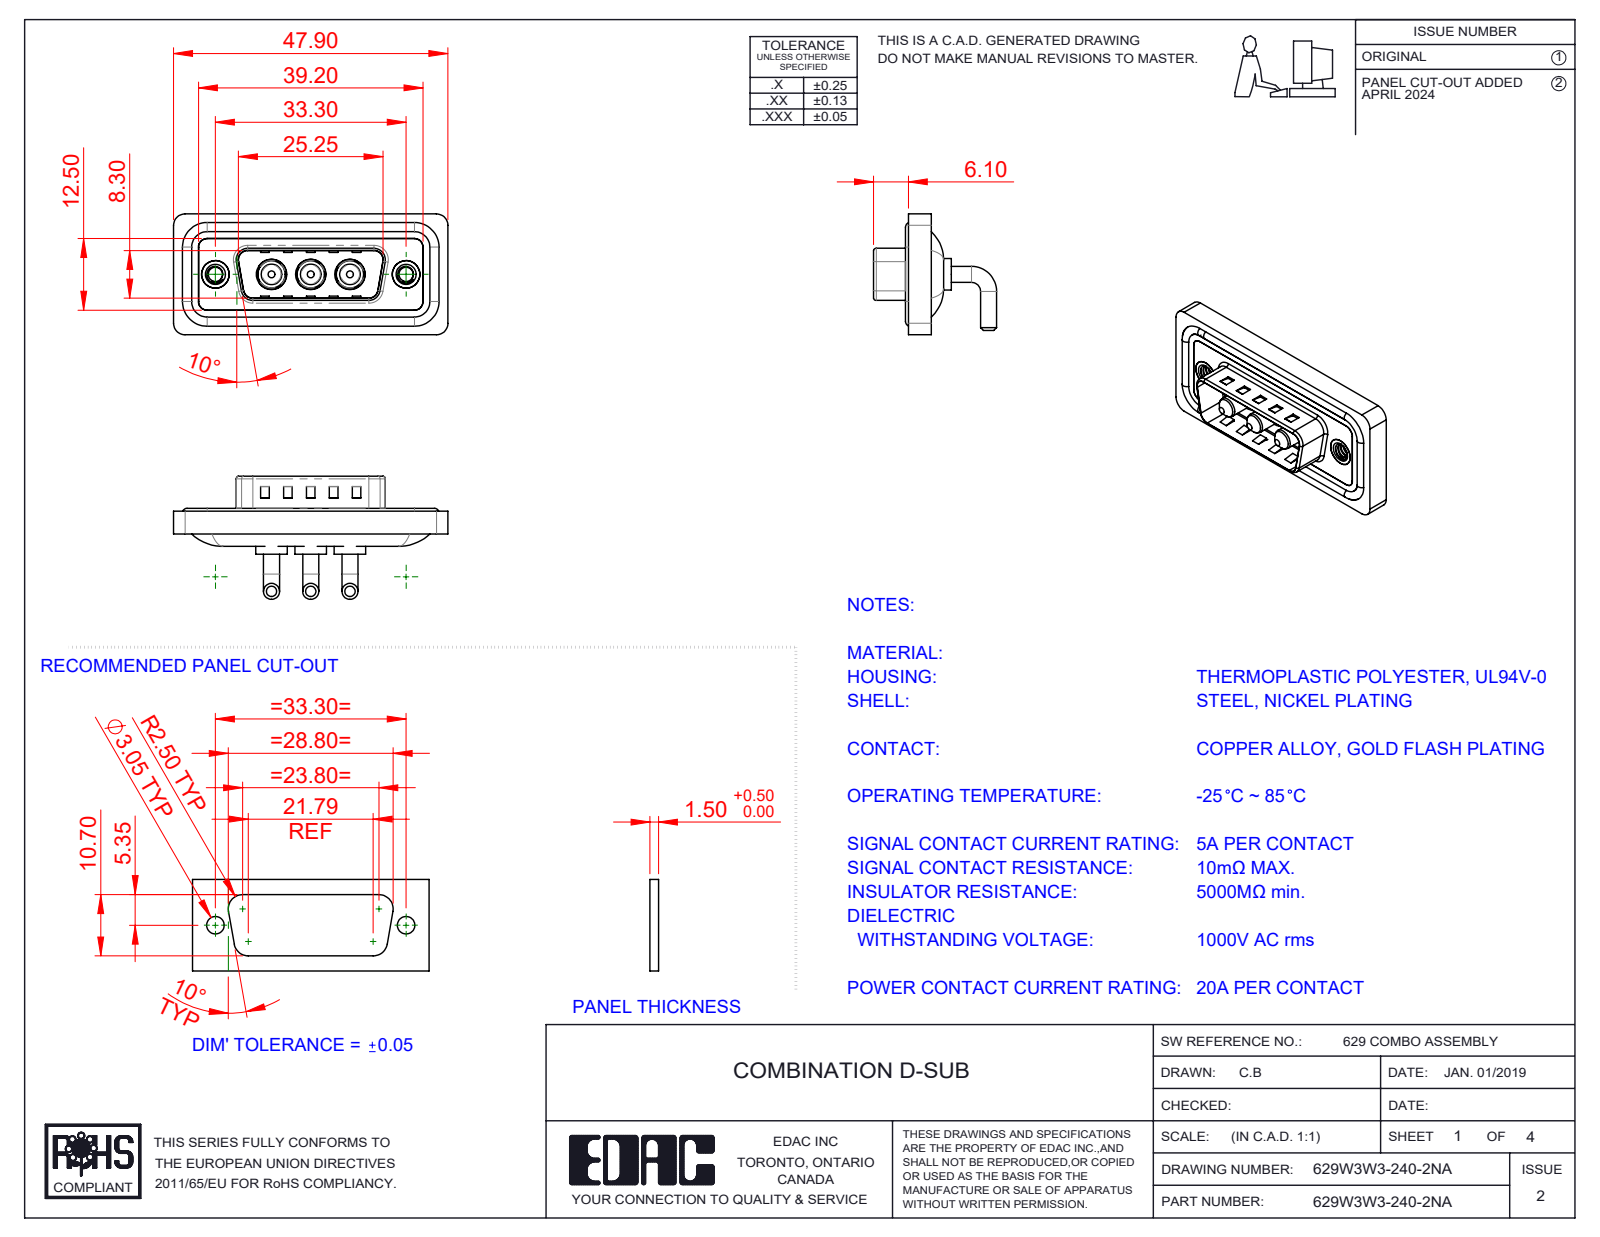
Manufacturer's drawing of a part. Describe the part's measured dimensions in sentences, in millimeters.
The part is named "629Combo Shell Rear_15 Contacts; 629Combo Shell Front_15 Contacts; 629W3W3-140-2NA; 629Combo Waterproof Housing_15 Contacts (+3 more)". Its 3-D file was written by "SolidWorks 2023 (CONFIG_CONTROL_DESIGN)". It is 13 solids with 570 faces: 207 planar, 245 cylindrical and 118 other. Overall it measures 47.9 by 21.5 by 21.1 millimeters. Its volume is 5 782 cubic millimeters and its surface area 9 040 square millimeters. Round holes: 3 of diameter 4.85, 3 of diameter 5.3, 2 of diameter 2.5, 2 of diameter 4, 2 of diameter 4.8, 2 of diameter 5. Round bosses or shafts: 6 of diameter 2.8, 4 of diameter 1.6, 3 of diameter 5.5, 3 of diameter 5.2, 3 of diameter 4.75, 3 of diameter 3.75, 3 of diameter 3.6, 2 of diameter 4.9. Partial cylindrical surfaces (rounded edges, fillets, slot ends): 20 of radius 2, 18 of radius 1.5, 8 of radius 0.5, 8 of radius 1.6, 4 of radius 0.25, 4 of radius 0.6, 4 of radius 0.65, 4 of radius 0.9. The main face-to-face distances are 0.4, 2.9, 0.8, 1.1, 2.1, 1.6, 3.1, 2.5, 4.5, 3.7. The hole center spacings are 6.85, 9.8, 16.65, 23.5, 13.7, 33.3.
